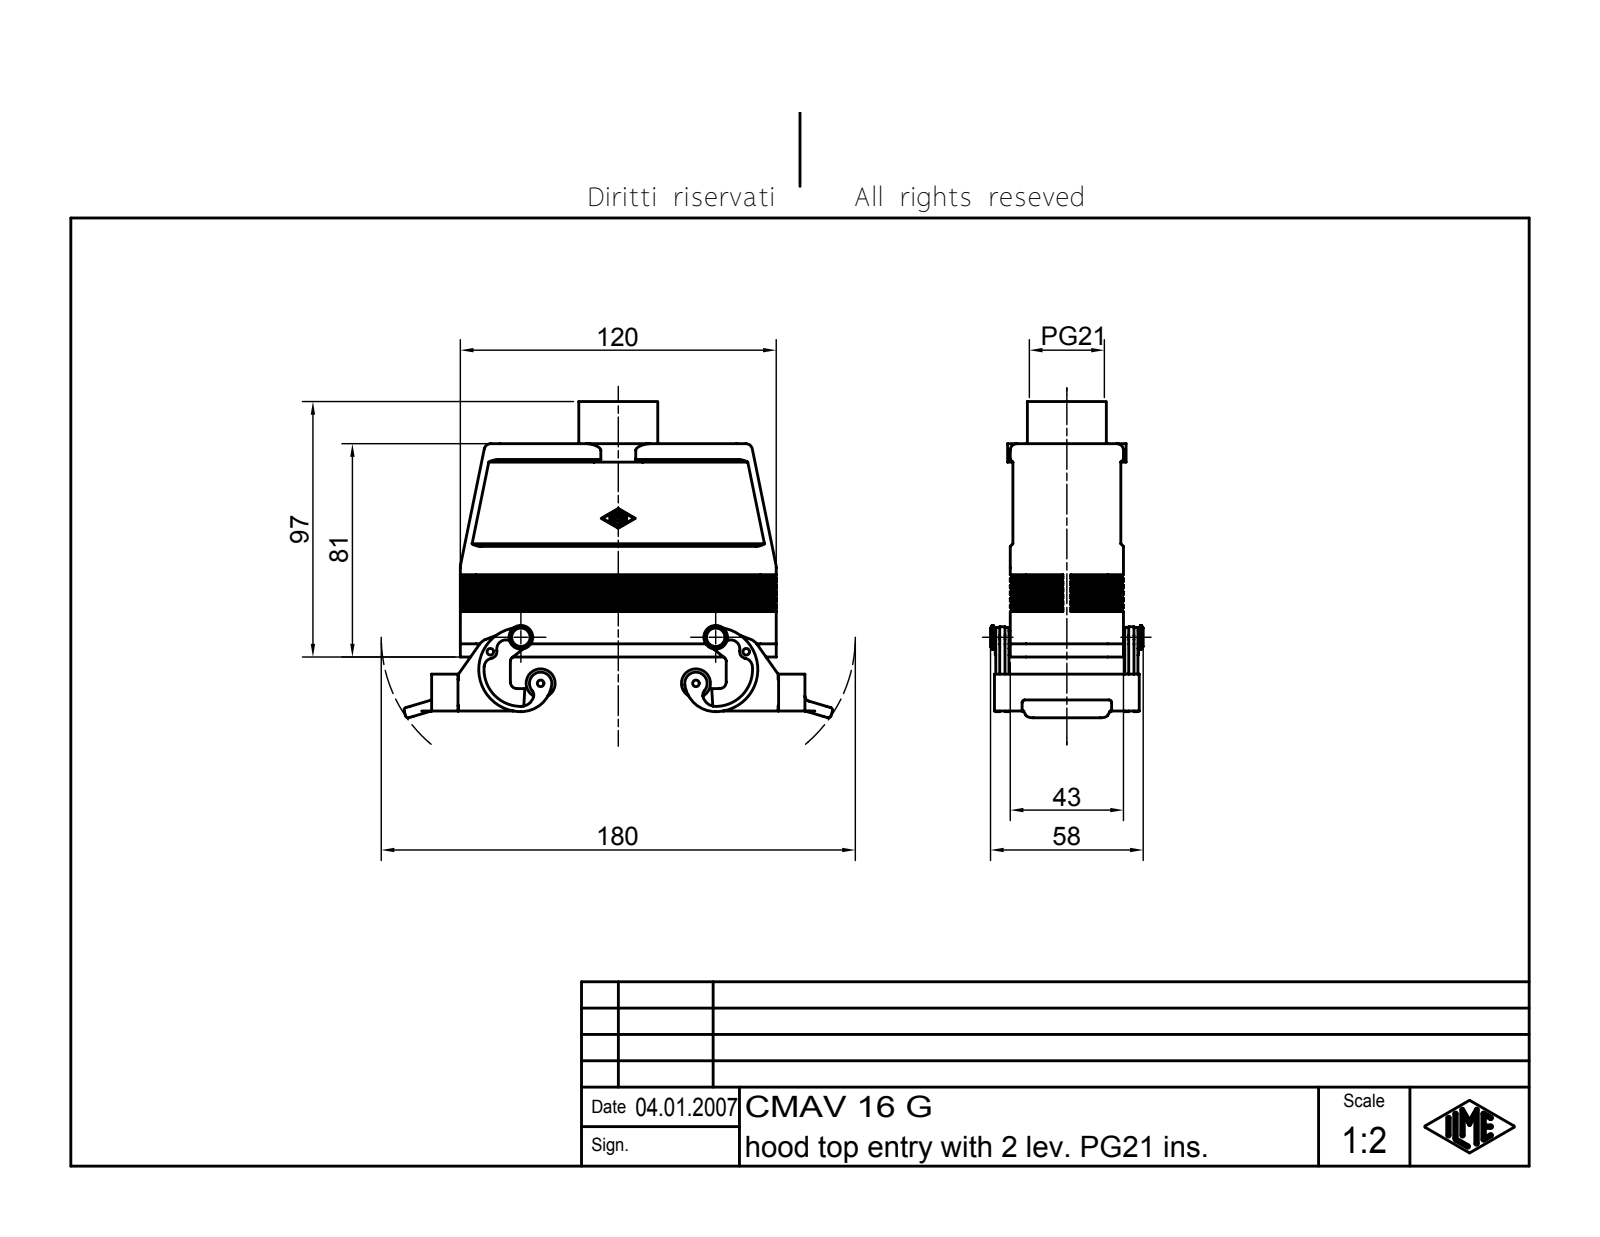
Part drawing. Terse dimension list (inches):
name: CAV Tüllengehäuse 2 Bügel für einen Einsatz
written by: Autodesk Inventor 7 (AUTOMOTIVE_DESIGN)
unit: in
bodies: 1 solid, 965 faces (302 planar, 256 cylindrical, 407 other)
size: 6.409 × 4.728 × 2.283
volume: 7.955 in³; area: 117 in²
holes: 2× ⌀0.098, 1× ⌀0.976, 1× ⌀1.054
bosses: 2× ⌀0.433, 2× ⌀0.354, 2× ⌀0.197, 2× ⌀0.079, 1× ⌀1.772, 1× ⌀1.181
rounds: 14× R0.01, 12× R0.039, 10× R0.098, 10× R0.236, 8× R0.118, 7× R0.079, 4× R0.138, 4× R0.197
face distances: 0.157, 0.118, 1.535, 1.378, 1.496, 0.039, 1.654, 1.693, 1.614, 0.276
hole spacings: 3.827
